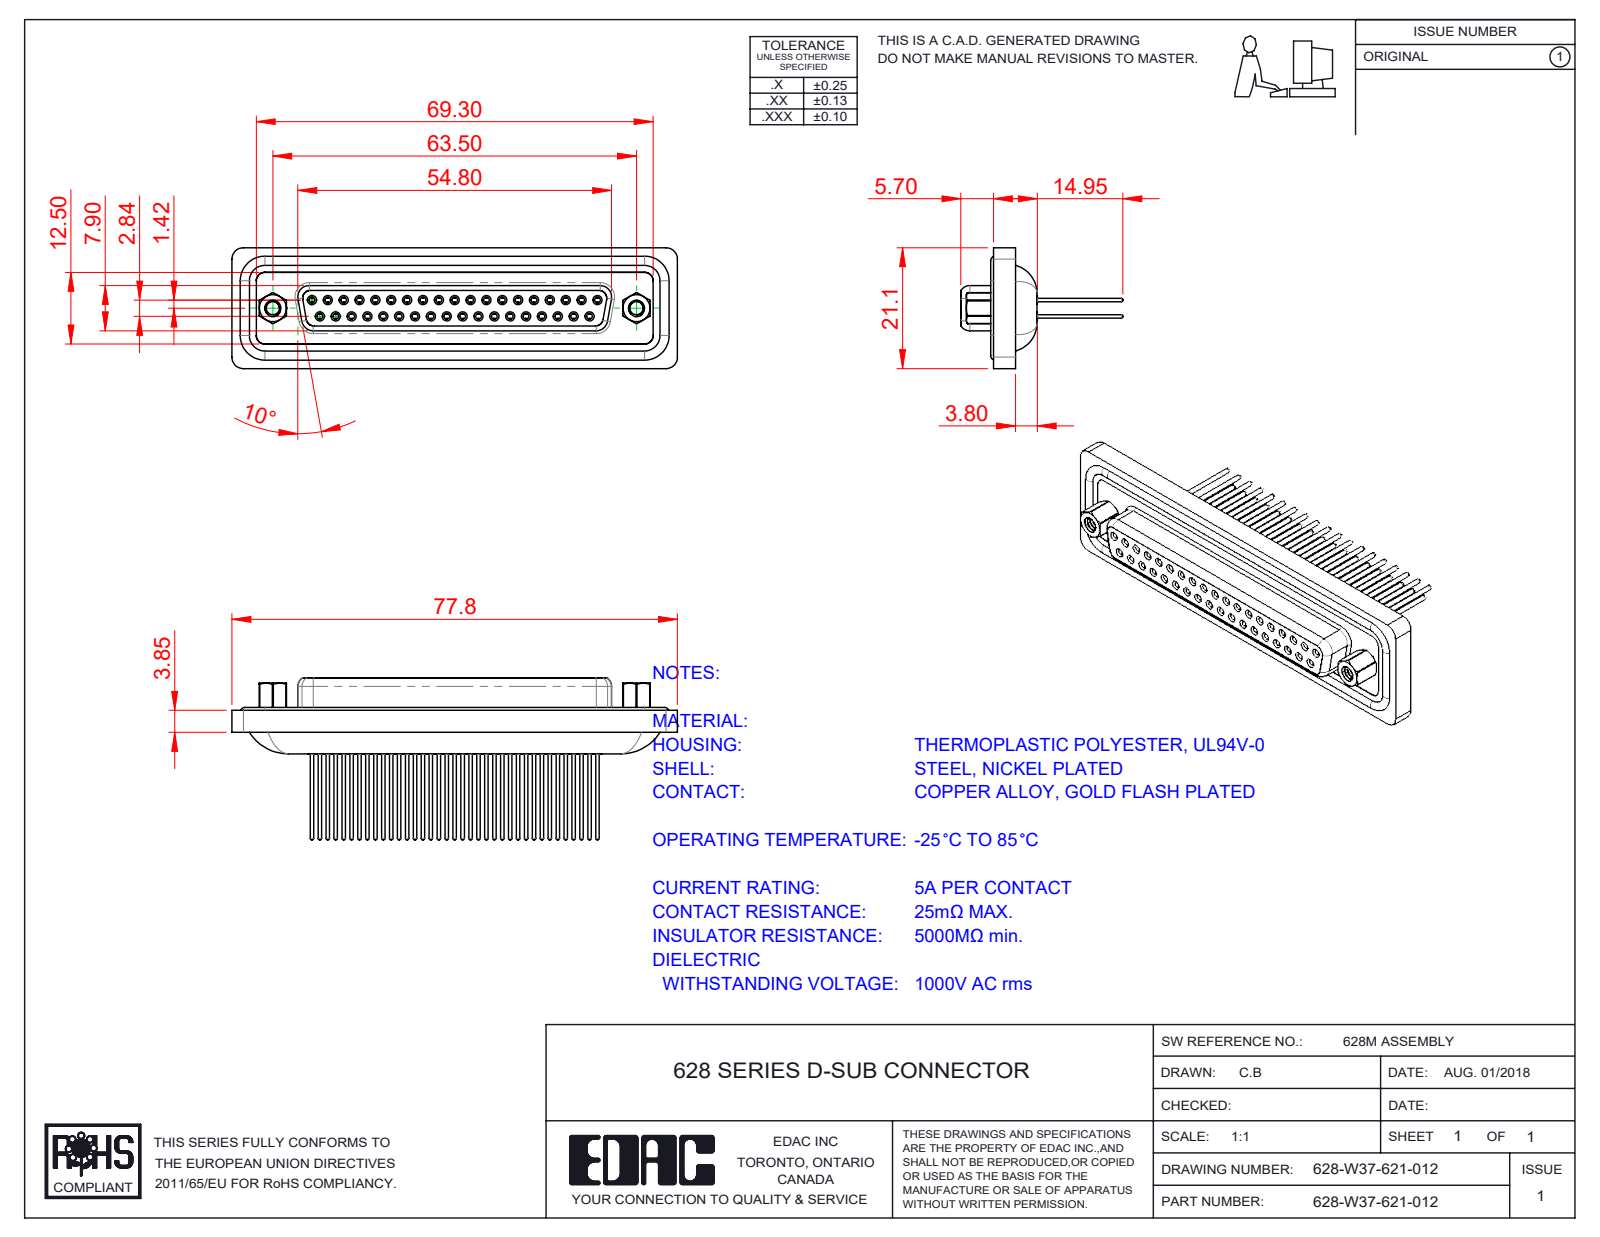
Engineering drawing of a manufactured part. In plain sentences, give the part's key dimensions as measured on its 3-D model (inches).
The part is named "628W 4-40 Hex Standoff; 628W Waterproof Housing_37 Contacts; 628W Housing_37 Contacts; 628W Shell Front_37 Contacts (+4 more)". Its 3-D file was written by "SolidWorks 2020 (CONFIG_CONTROL_DESIGN)". It is 45 solids with 2532 faces: 656 planar, 997 cylindrical and 879 other. Overall it measures 3.063 by 1.114 by 0.831 inches. Its volume is 0.681 cubic inches and its surface area 28.79 square inches. Round holes: 37 of diameter 0.039, 37 of diameter 0.043, 37 of diameter 0.059, 37 of diameter 0.067, 37 of diameter 0.071, 37 of diameter 0.079, 2 of diameter 0.089, 2 of diameter 0.09, 2 of diameter 0.157, 2 of diameter 0.189, 2 of diameter 0.197. Round bosses or shafts: 41 of diameter 0.063, 37 of diameter 0.087, 37 of diameter 0.024, 8 of diameter 0.059, 2 of diameter 0.193, 2 of diameter 0.11. Partial cylindrical surfaces (rounded edges, fillets, slot ends): 16 of radius 0.079, 14 of radius 0.059, 8 of radius 0.053, 6 of radius 0.106, 4 of radius 0.02, 4 of radius 0.035, 4 of radius 0.063, 4 of radius 0.069. The main face-to-face distances are 0.016, 0.293, 0.295, 0.333, 0.244, 0.537, 0.148, 0.161, 0.043, 0.108. The hole center spacings are 0.124, 0.109, 0.218, 0.327, 0.198, 0.295, 0.436, 0.545.
